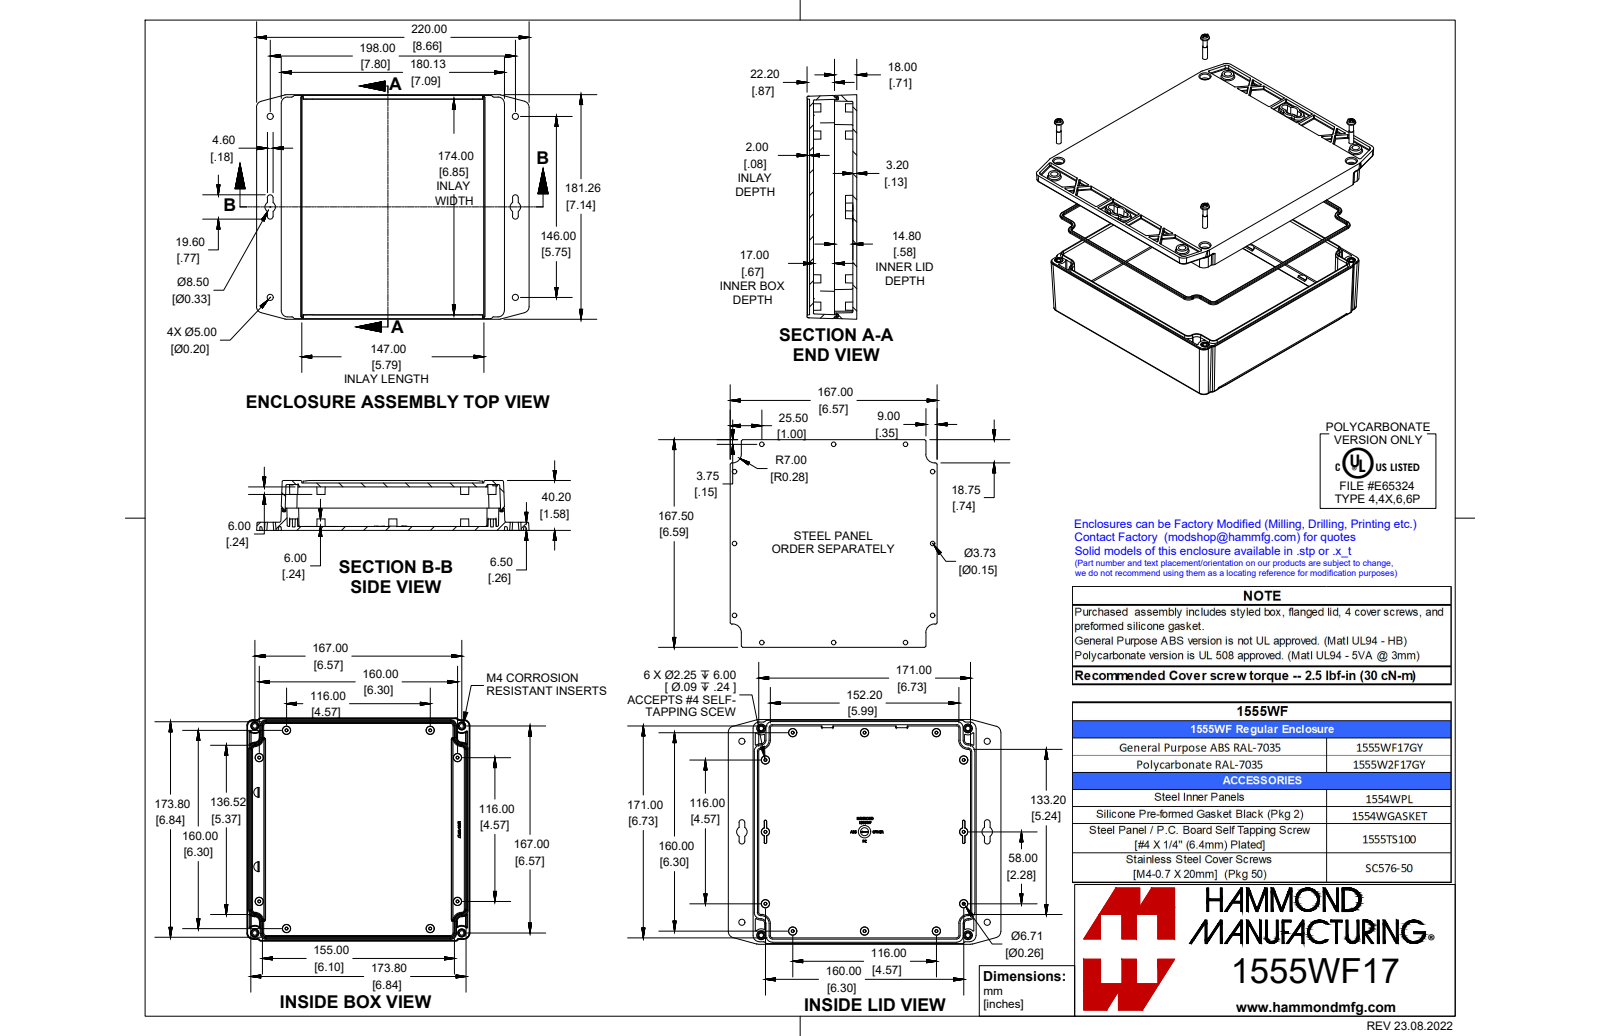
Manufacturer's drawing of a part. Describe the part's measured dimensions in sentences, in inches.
The part is named "1555W2F17GY". Its 3-D file was written by "SolidWorks 2021 (AUTOMOTIVE_DESIGN)". It is 7 solids with 1418 faces: 471 planar, 347 cylindrical and 600 other. Overall it measures 8.661 by 7.141 by 1.583 inches. Its volume is 20.88 cubic inches and its surface area 341.2 square inches. Round holes: 4 of diameter 0.128, 4 of diameter 0.158. Round bosses or shafts: 4 of diameter 0.276, 4 of diameter 0.153, 4 of diameter 0.138. Partial cylindrical surfaces (rounded edges, fillets, slot ends): 130 of radius 0.02, 45 of radius 0.031, 16 of radius 0.012, 8 of radius 0.039, 8 of radius 0.104, 8 of radius 0.197, 8 of radius 0.199, 4 of radius 0.118. The main face-to-face distances are 0.126, 1.378, 1.504, 1.252, 0.122, 0.13, 1.327, 0.118, 0.256, 1.248. The hole center spacings are 6.575, 9.298.
